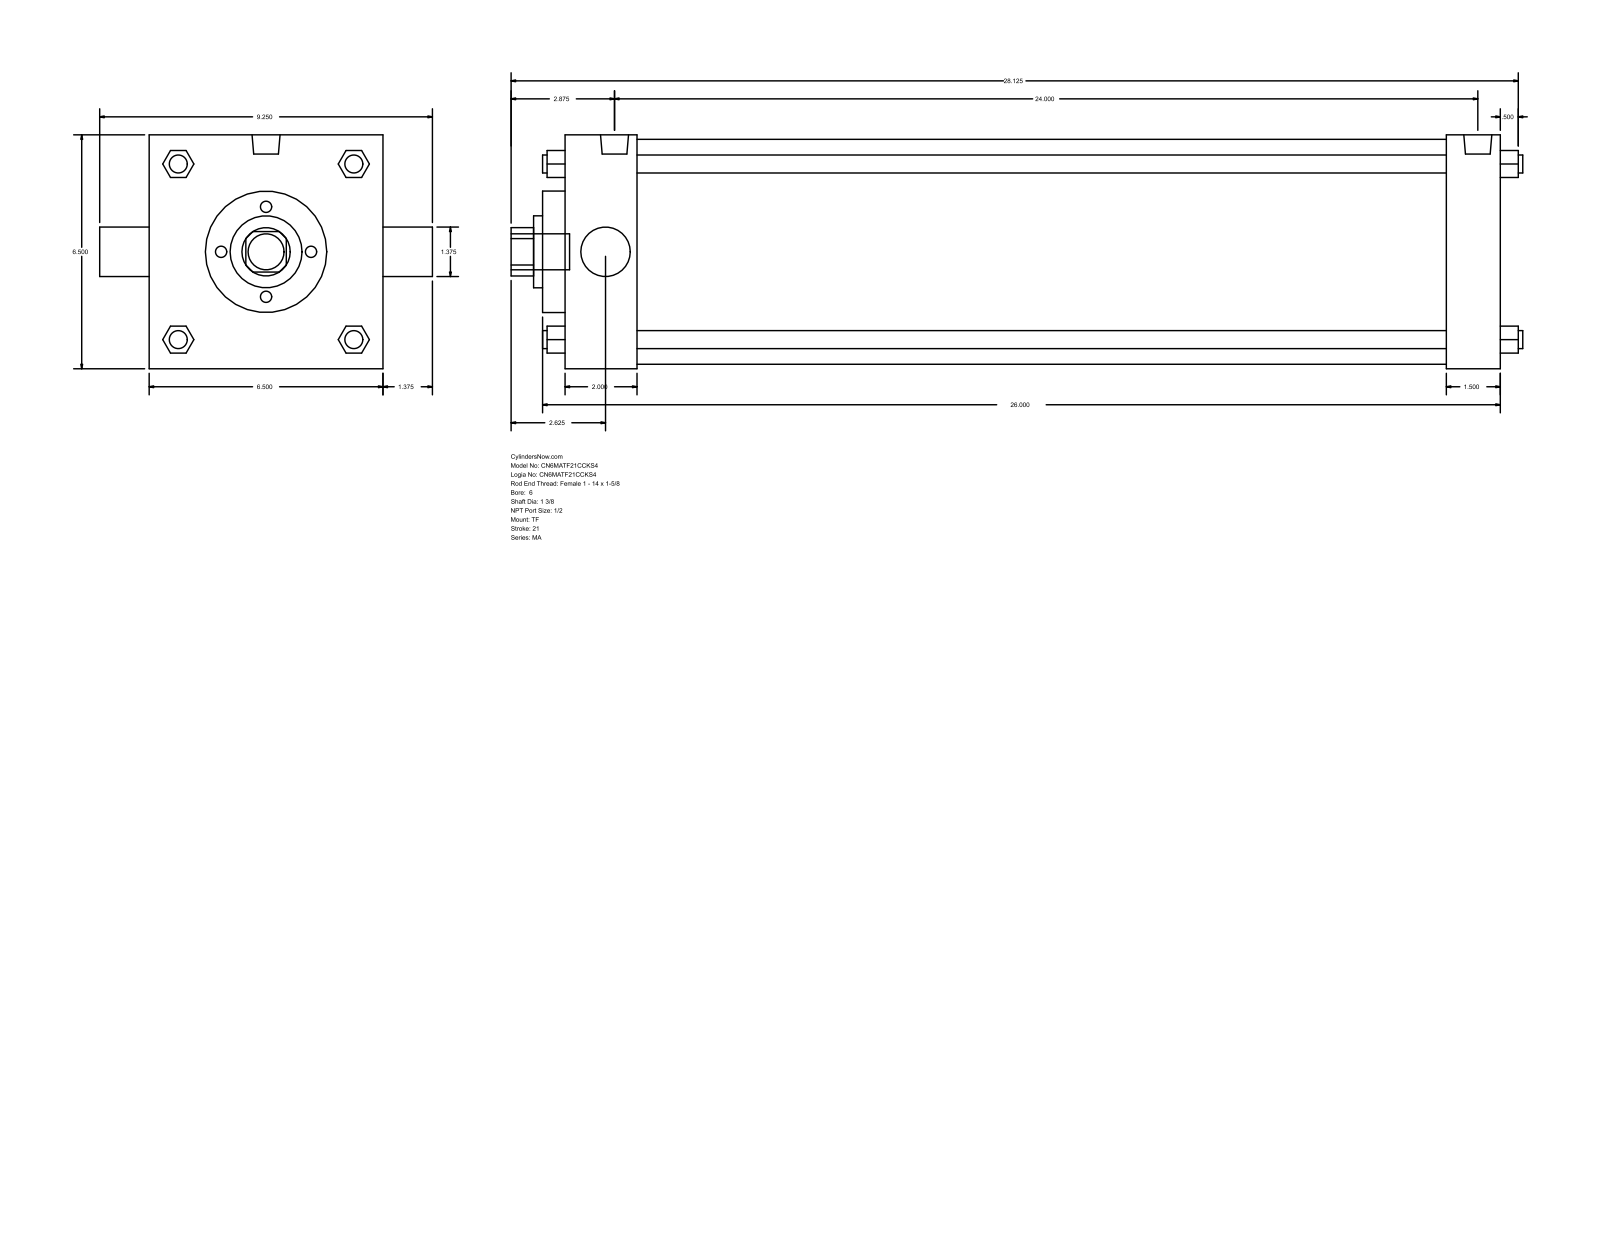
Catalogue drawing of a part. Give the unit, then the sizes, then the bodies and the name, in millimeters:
Units: millimetres
Overall size (bounding box): 714.38 × 234.95 × 165.1
Round holes (diameter × count): ⌀34.92 ×2, ⌀50.8 ×1, ⌀85.72 ×1, ⌀158.75 ×1
Round bosses / shafts (diameter × count): ⌀12.7 ×4, ⌀17.46 ×3, ⌀19.77 ×2, ⌀25.4 ×1
Partial cylindrical surfaces — rounded edges, fillets, slot ends (radius × count): R17.06 ×1
Main face-to-face distances: 165.1, 663.57, 50.8, 625.48, 612.77, 574.68, 38.09, 15.87, 66.67, 641.35
Bodies: 0 solids, 122 faces (93 planar, 29 cylindrical, 0 other)
Part name (STEP PRODUCT): MA_TF__0600_1.375
STEP written by: GSSL Pune (CONFIG_CONTROL_DESIGN)
